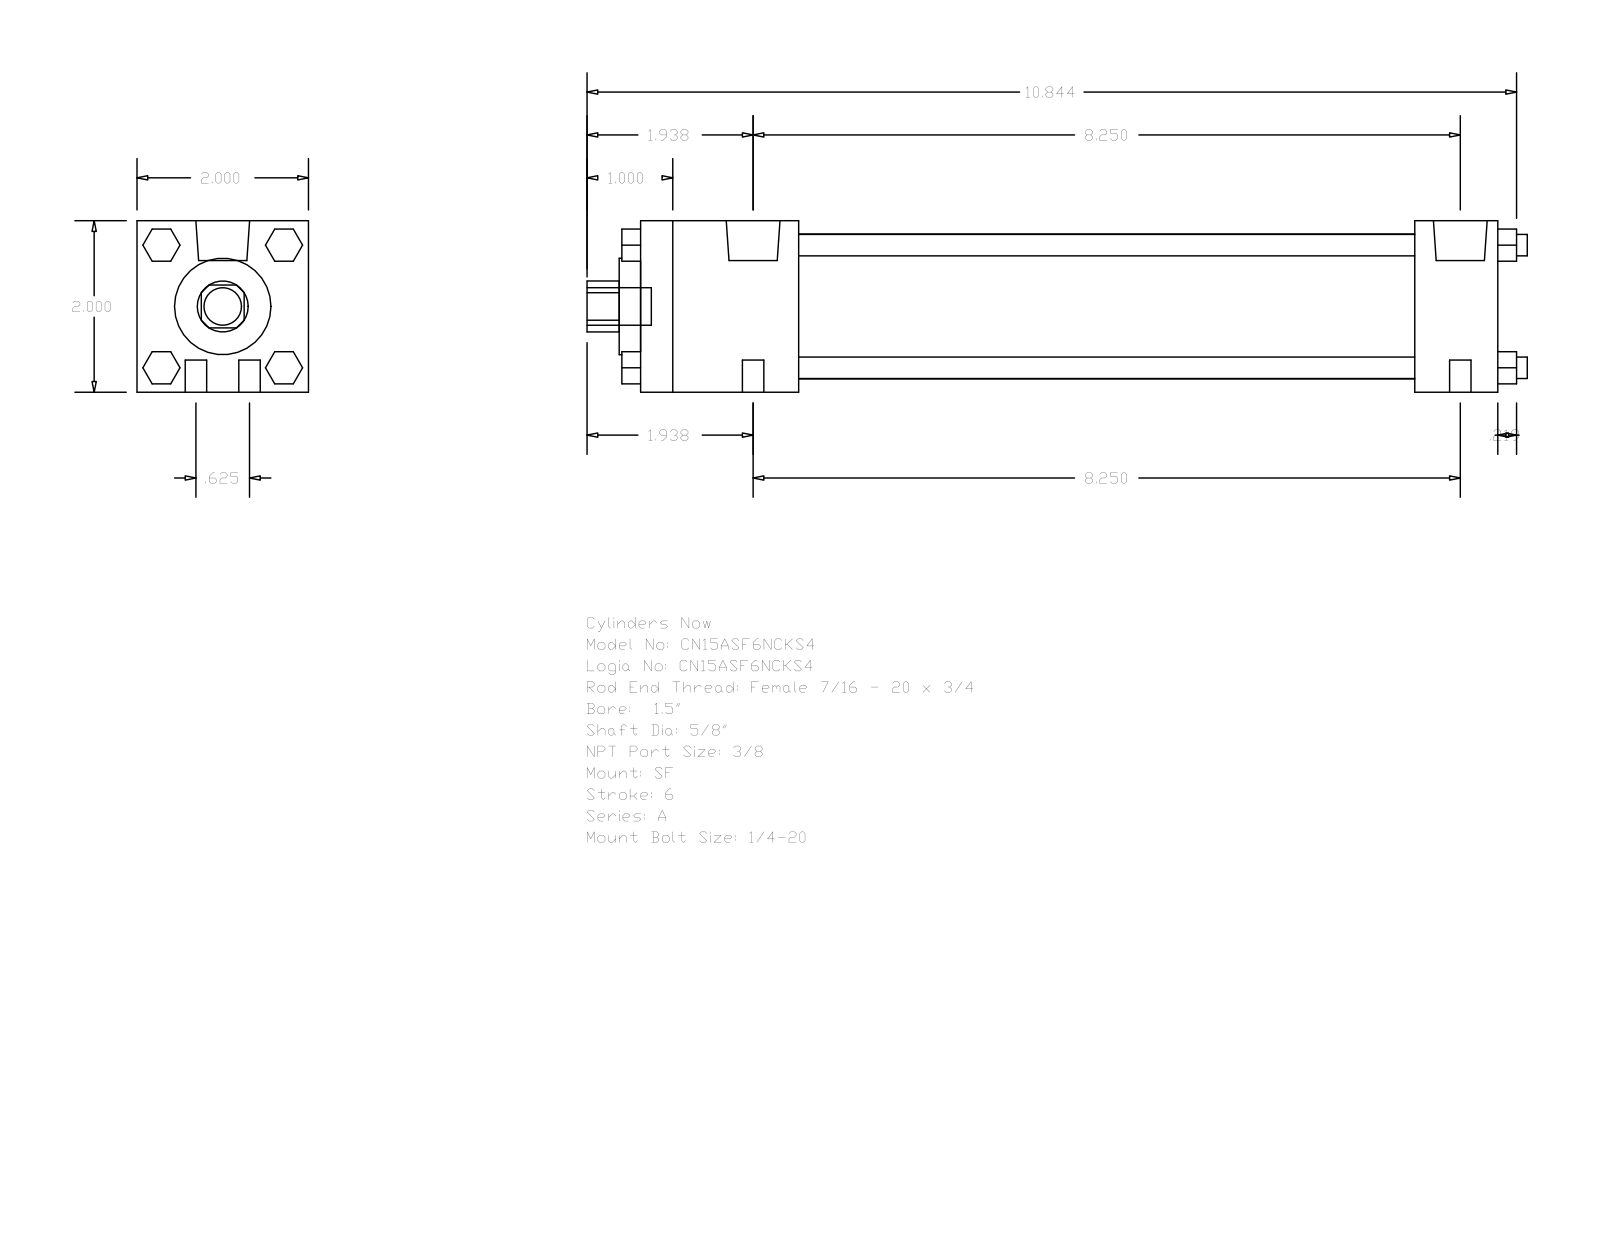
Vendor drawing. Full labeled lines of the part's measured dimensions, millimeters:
Part name (STEP PRODUCT): A_SF__0150_0.625
STEP written by: GSSL Pune (CONFIG_CONTROL_DESIGN)
Units: millimetres
Bodies: 0 solids, 124 faces (94 planar, 30 cylindrical, 0 other)
Overall size (bounding box): 278.61 × 50.8 × 50.8
Round holes (diameter × count): ⌀15.88 ×1, ⌀28.57 ×1, ⌀42.93 ×1
Round bosses / shafts (diameter × count): ⌀6.35 ×8, ⌀15.93 ×2, ⌀5.56 ×2, ⌀11.11 ×1
Partial cylindrical surfaces — rounded edges, fillets, slot ends (radius × count): R7.54 ×1
Main face-to-face distances: 50.8, 254, 46.83, 229.39, 182.56, 207.17, 24.61, 9.52, 6.35, 53.18
